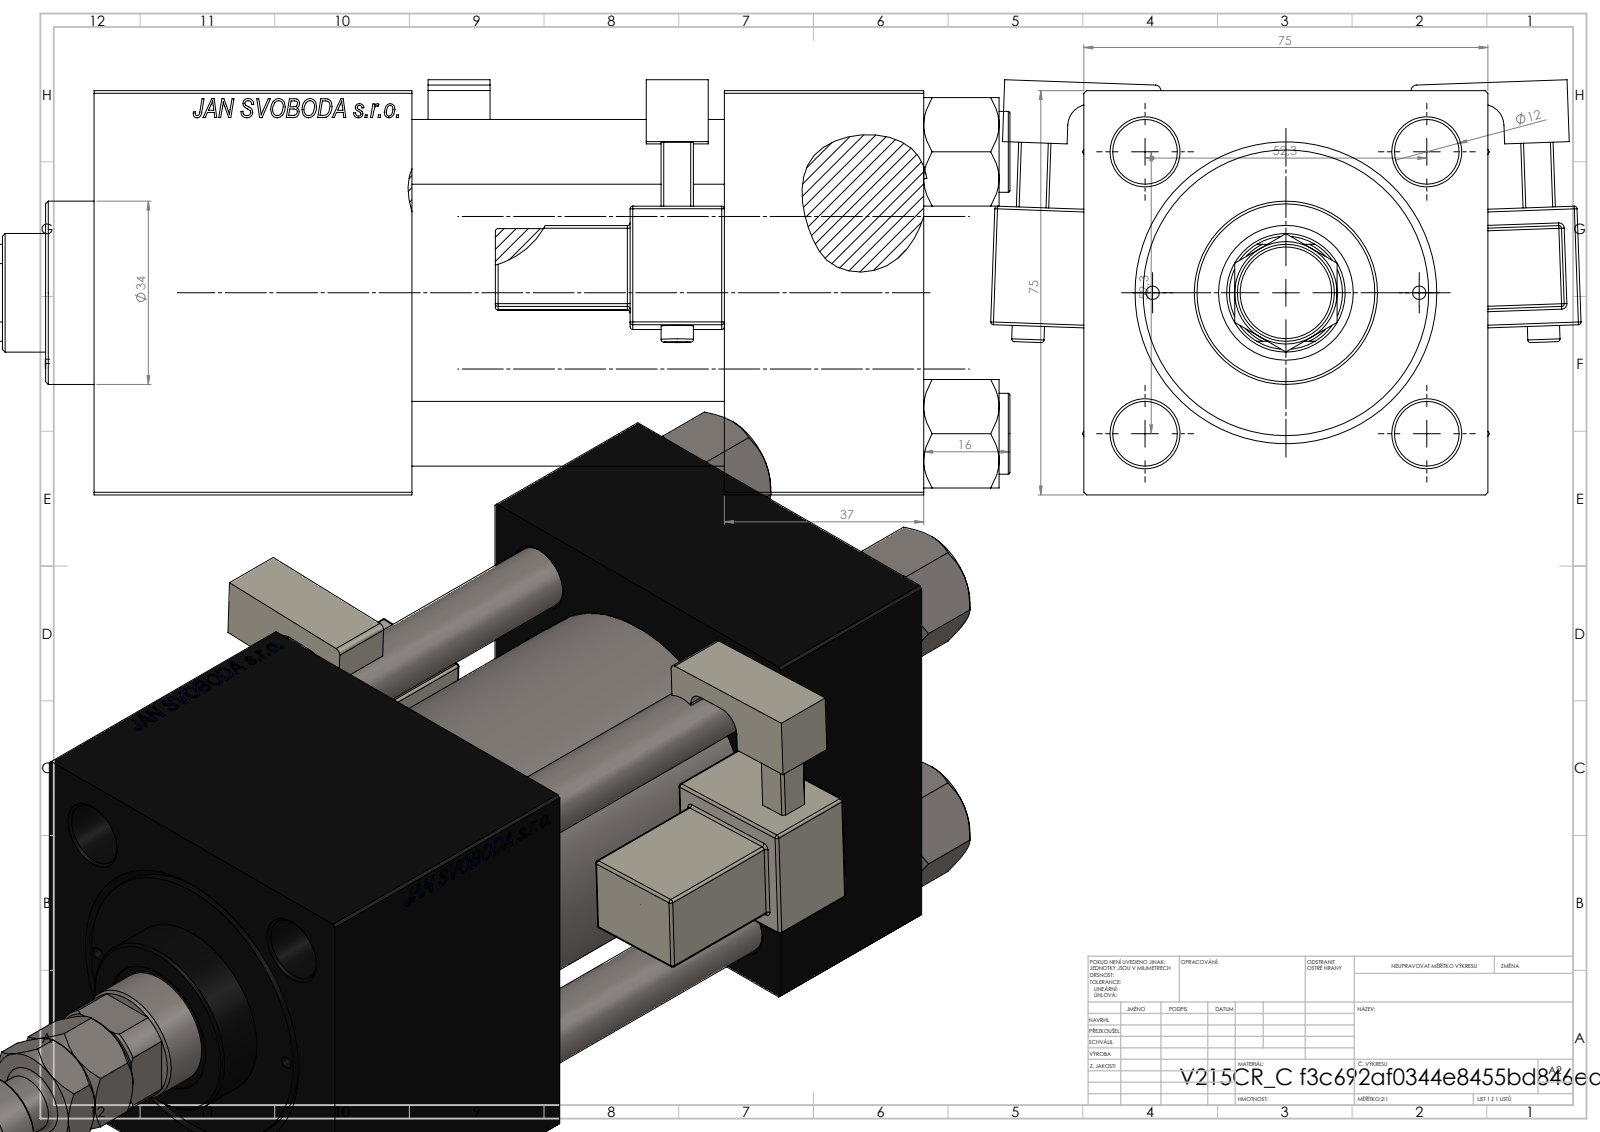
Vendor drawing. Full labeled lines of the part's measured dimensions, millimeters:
Part name (STEP PRODUCT): V215CR_C_TYCINKA; NUT_M5_C; V215_VC_A; V215CR_MSU (+3 more)
STEP written by: SolidWorks 2019 (CONFIG_CONTROL_DESIGN)
Units: millimetres
Bodies: 14 solids, 1360 faces (602 planar, 154 cylindrical, 604 other)
Overall size (bounding box): 228 × 109.57 × 77.03
Volume: 706 129 mm³ · Surface area: 162 330 mm²
Round holes (diameter × count): ⌀12 ×4, ⌀2.5 ×2, ⌀7 ×2, ⌀20.96 ×2, ⌀30 ×2, ⌀10.5 ×1, ⌀22 ×1, ⌀25 ×1, ⌀41 ×1, ⌀50 ×1, ⌀53 ×1
Round bosses / shafts (diameter × count): ⌀15 ×4, ⌀6 ×2, ⌀56 ×1, ⌀34 ×1, ⌀18 ×1, ⌀11 ×1
Partial cylindrical surfaces — rounded edges, fillets, slot ends (radius × count): R0.5 ×48, R1 ×2, R2.5 ×2, R4 ×2, R10.5 ×1
Main face-to-face distances: 75, 37, 117, 58, 154, 95, 59, 125.3, 88.3, 30.3
Hole centre spacings: 26.19, 36.98, 52.3, 57.22, 24.75, 73.96, 49.5, 93.5
